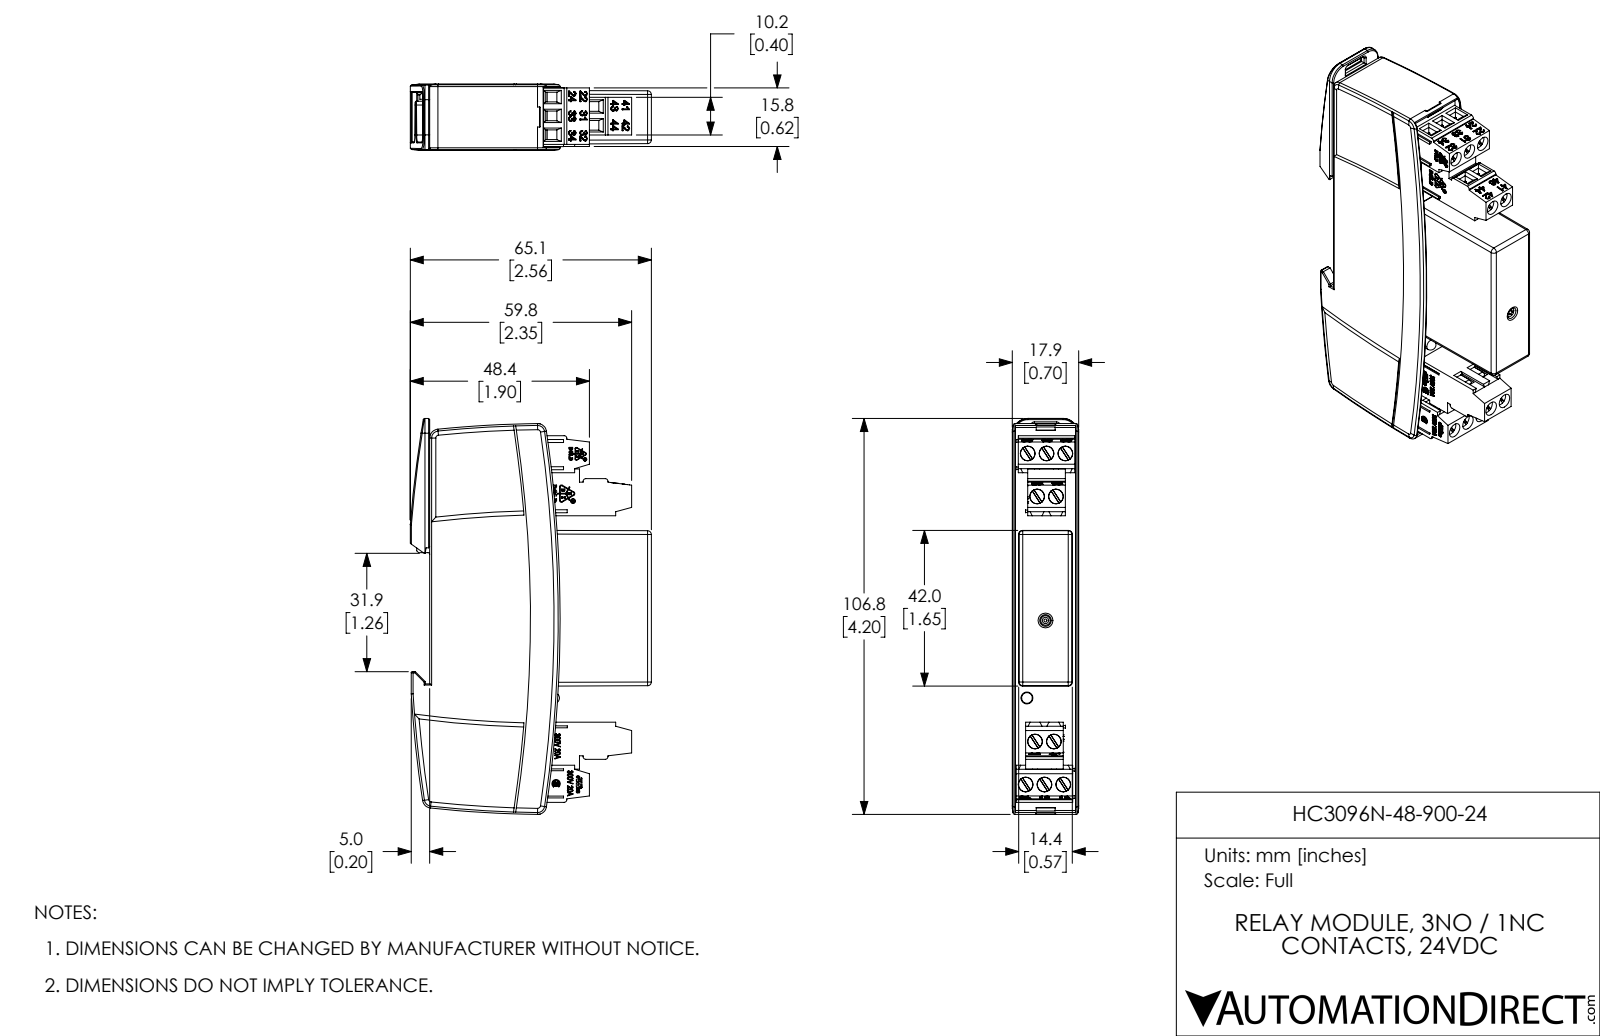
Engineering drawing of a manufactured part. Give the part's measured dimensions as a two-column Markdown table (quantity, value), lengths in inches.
| quantity | value |
| --- | --- |
| part name | HC3096N-48-900-24 |
| STEP written by | SolidWorks 2017 (AUTOMOTIVE_DESIGN) |
| units | inches |
| bodies | 1 solid, 3301 faces (2195 planar, 541 cylindrical, 565 other) |
| overall size | 4.204 × 2.561 × 0.705 |
| volume | 5.189 in³ |
| surface area | 36.51 in² |
| round holes (diameter × count) | 0.157 × 10, 0.022 × 4, 0.037 × 2, 0.05 × 2 |
| round bosses / shafts (diameter × count) | 0.154 × 10, 0.019 × 3, 0.046 × 2, 0.034 × 2, 0.126 × 1, 0.114 × 1, 0.031 × 1, 0.019 × 1 |
| partial cylindrical surfaces (radius × count) | 0.006 × 20, 0.012 × 11, 0.02 × 11, 0.005 × 10, 0.039 × 10, 0.004 × 8, 0.006 × 8, 0.031 × 8 |
| main face-to-face distances | 0.697, 0.705, 0.689, 0.033, 0.663, 0.671, 0.026, 1.177, 1.173, 0.022 |
| hole center spacings | 0.467, 0.2, 0.546, 3.059, 3.061, 3.515, 0.253, 0.4 |
